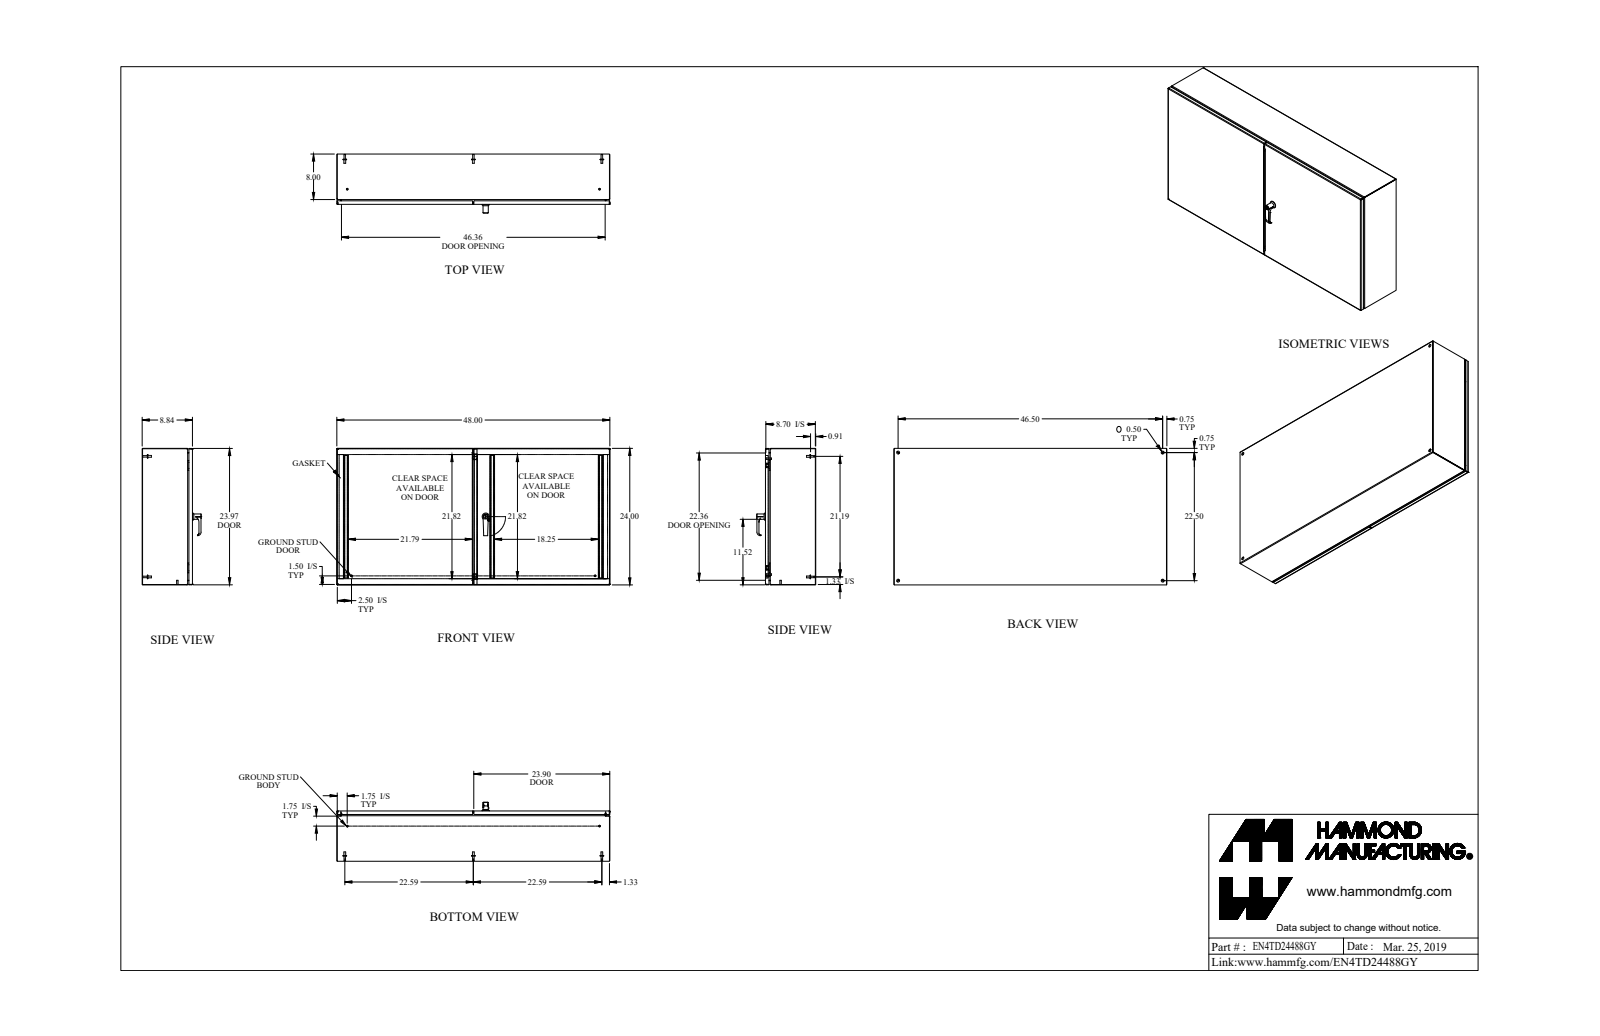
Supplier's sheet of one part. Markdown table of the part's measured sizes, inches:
| quantity | value |
| --- | --- |
| part name | EN4TD24488GY |
| STEP written by | SolidWorks 2018 (AUTOMOTIVE_DESIGN) |
| units | inches |
| bodies | 77 solids, 1935 faces (883 planar, 714 cylindrical, 338 other) |
| overall size | 48 × 24 × 10.372 |
| volume | 320 in³ |
| surface area | 8 300 in² |
| round holes (diameter × count) | 0.196 × 5, 0.176 × 4, 0.265 × 4, 0.5 × 4, 0.24 × 3, 0.242 × 3, 0.172 × 2, 0.25 × 2, 0.256 × 2, 0.26 × 2, 0.313 × 2, 0.394 × 2 |
| round bosses / shafts (diameter × count) | 0.25 × 12, 0.313 × 8, 0.625 × 6, 0.27 × 6, 0.51 × 4, 0.281 × 4, 0.156 × 4, 0.75 × 3 |
| partial cylindrical surfaces (radius × count) | 0.036 × 26, 0.108 × 26, 0.094 × 20, 0.043 × 18, 0.062 × 18, 0.081 × 18, 0.02 × 16, 0.016 × 15 |
| main face-to-face distances | 0.072, 8.77, 8.698, 8.842, 23.928, 23.856, 47.928, 24, 47.856, 48 |
| hole center spacings | 0.787, 10.188, 20.798, 22.5, 23.896, 25.752, 27.796, 46.5 |
